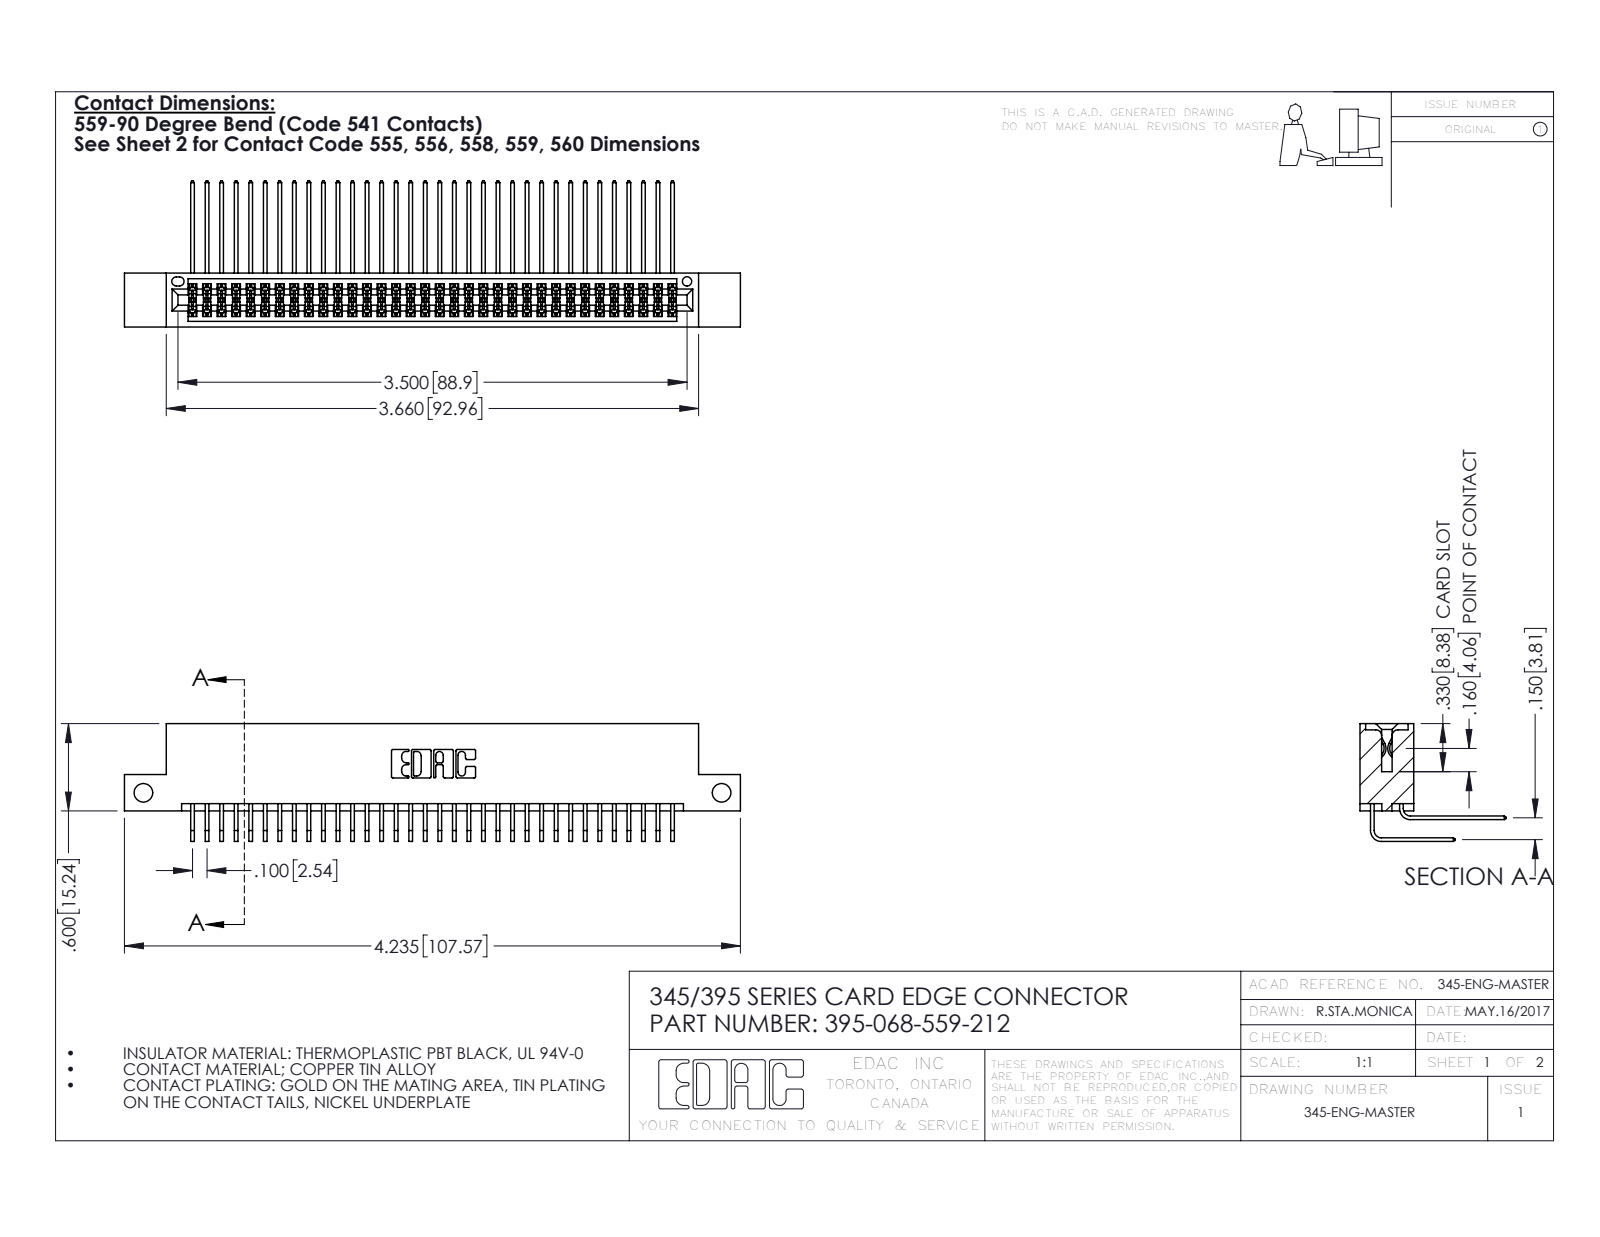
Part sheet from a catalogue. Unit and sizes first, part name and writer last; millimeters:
Units: millimetres
Overall size (bounding box): 107.6 × 25.5 × 20.5
Round holes (diameter × count): ⌀3.3 ×2, ⌀1.6 ×1
Partial cylindrical surfaces — rounded edges, fillets, slot ends (radius × count): R0.2 ×103, R0.3 ×22, R0.2 ×6, R0.8 ×6, R0.7 ×3, R0.4 ×2, R0.5 ×2, R0.6 ×2
Main face-to-face distances: 1.8, 7.6, 5.1, 9.4, 2.5, 6.9, 0.6, 5.7, 4.4, 3.8
Hole centre spacings: 101
Volume: 10 700 mm³ · Surface area: 17 340 mm²
Bodies: 69 solids, 3662 faces (2460 planar, 1202 cylindrical, 0 other)
Part name (STEP PRODUCT): 395-068-559-212; 345-292-001_558 559 Tail - 1; 345-292-001_559 Tail - 2; 345 Part_Flush Mounting Lugs - Side Mount
STEP written by: SolidWorks 2016 (CONFIG_CONTROL_DESIGN)
